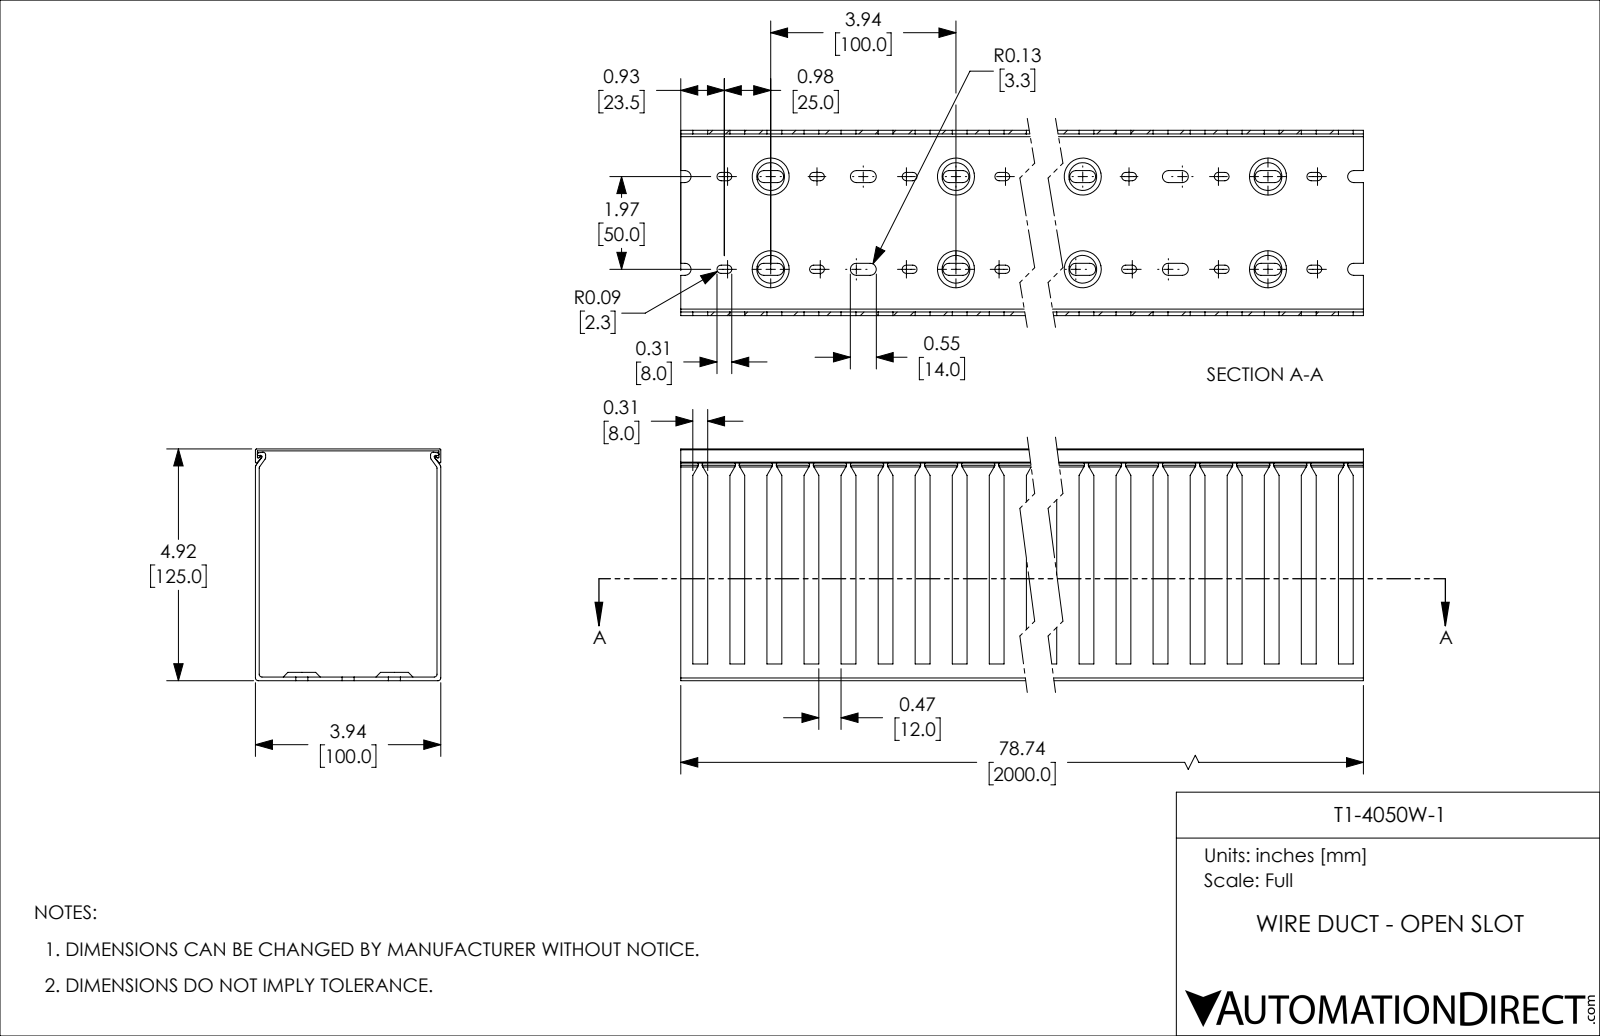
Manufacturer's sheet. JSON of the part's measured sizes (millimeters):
{"part_name": "T1-4050W-1", "step_written_by": "SolidWorks 2021 (CONFIG_CONTROL_DESIGN)", "units": "millimeters", "bodies": {"solids": 2, "faces": 1573, "planar": 762, "cylindrical": 731, "other": 80}, "overall_size": [2000, 125, 100], "volume_mm3": 1590000, "surface_area_mm2": 1833000, "partial_cylinders_radius": [[3.25, 200], [2.25, 160], [1.5, 12], [0.5, 8], [0.75, 6]], "face_to_face_distances": [2, 98, 100, 1, 96, 124, 125, 122, 123, 99]}
